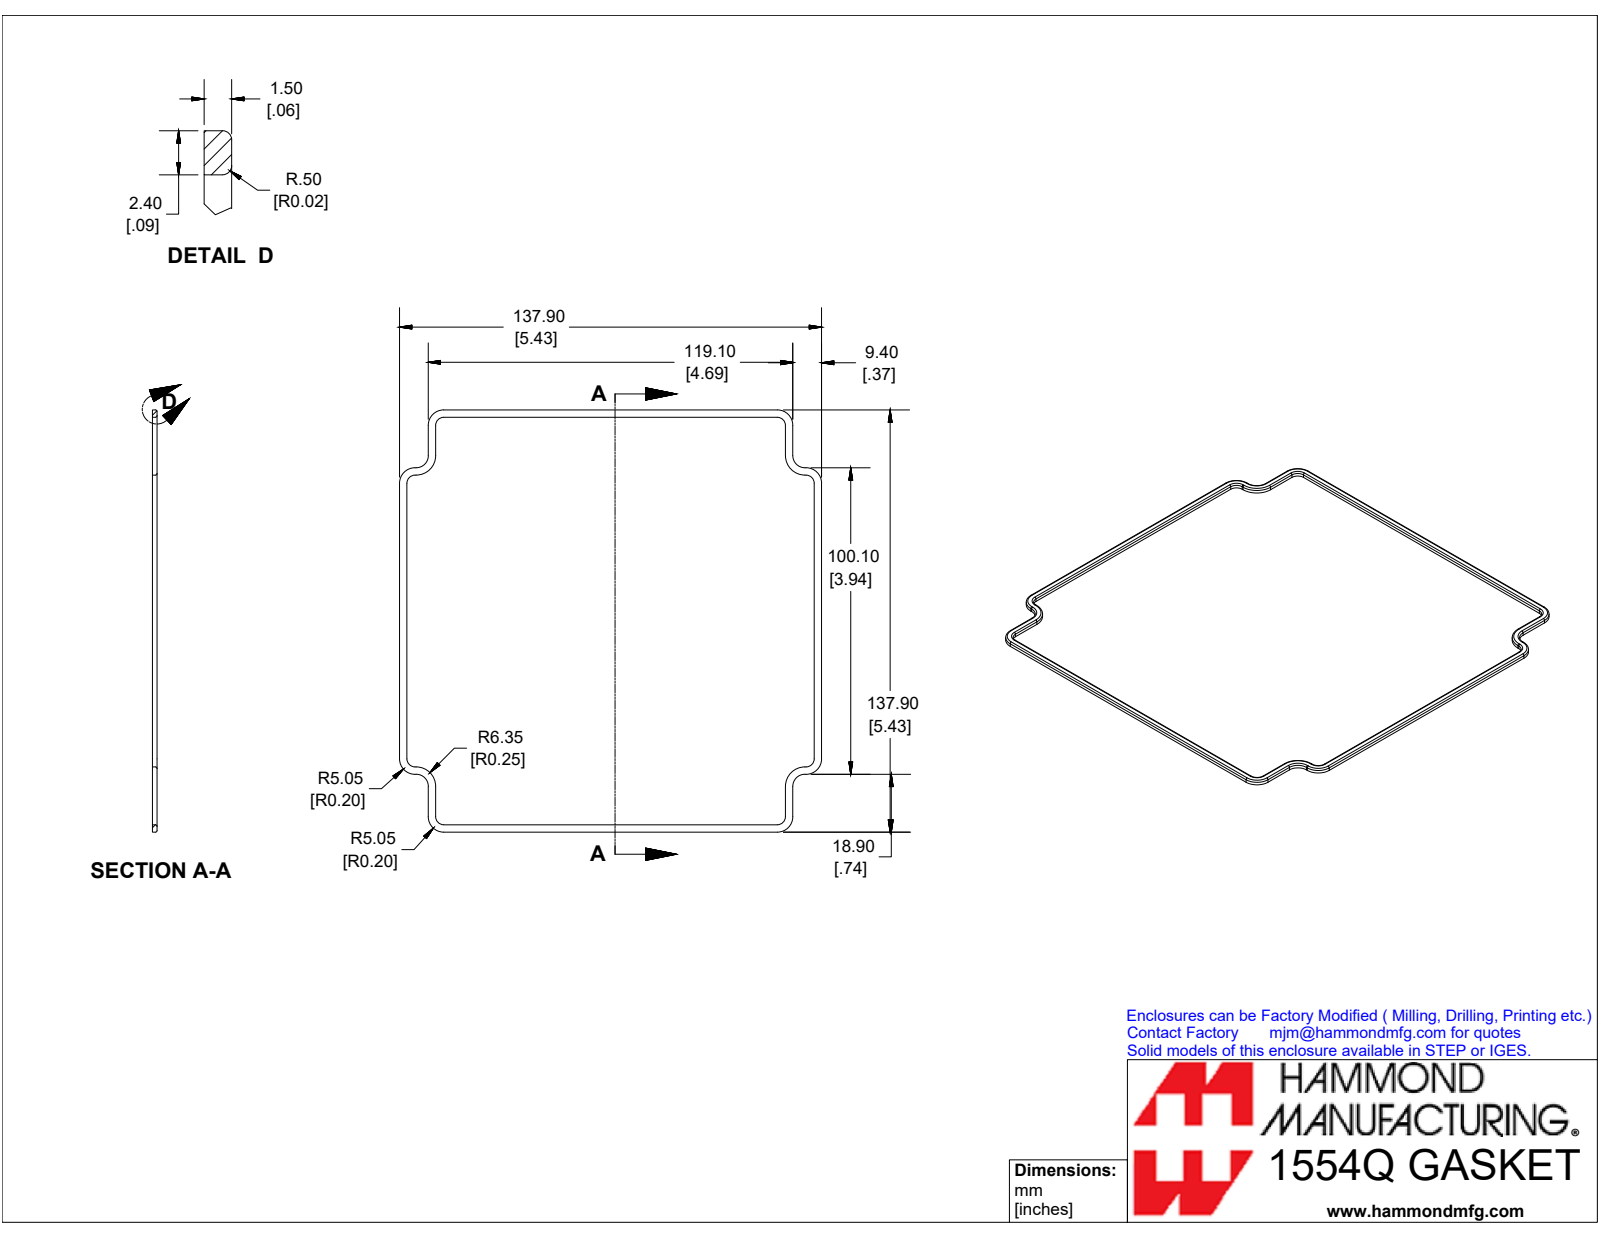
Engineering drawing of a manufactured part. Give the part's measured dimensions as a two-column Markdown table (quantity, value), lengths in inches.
| quantity | value |
| --- | --- |
| part name | 1554QGASKET |
| STEP written by | SolidWorks 2019 (CONFIG_CONTROL_DESIGN) |
| units | inches |
| bodies | 1 solid, 98 faces (26 planar, 48 cylindrical, 24 other) |
| overall size | 5.429 × 5.429 × 0.059 |
| volume | 0.111 in³ |
| surface area | 5.94 in² |
| partial cylindrical surfaces (radius × count) | 0.02 × 16, 0.104 × 8, 0.199 × 8, 0.156 × 4, 0.25 × 4 |
| main face-to-face distances | 0.059, 0.094, 5.335, 5.24, 5.429, 0.37, 4.965, 0.465, 4.87, 5.059 |
